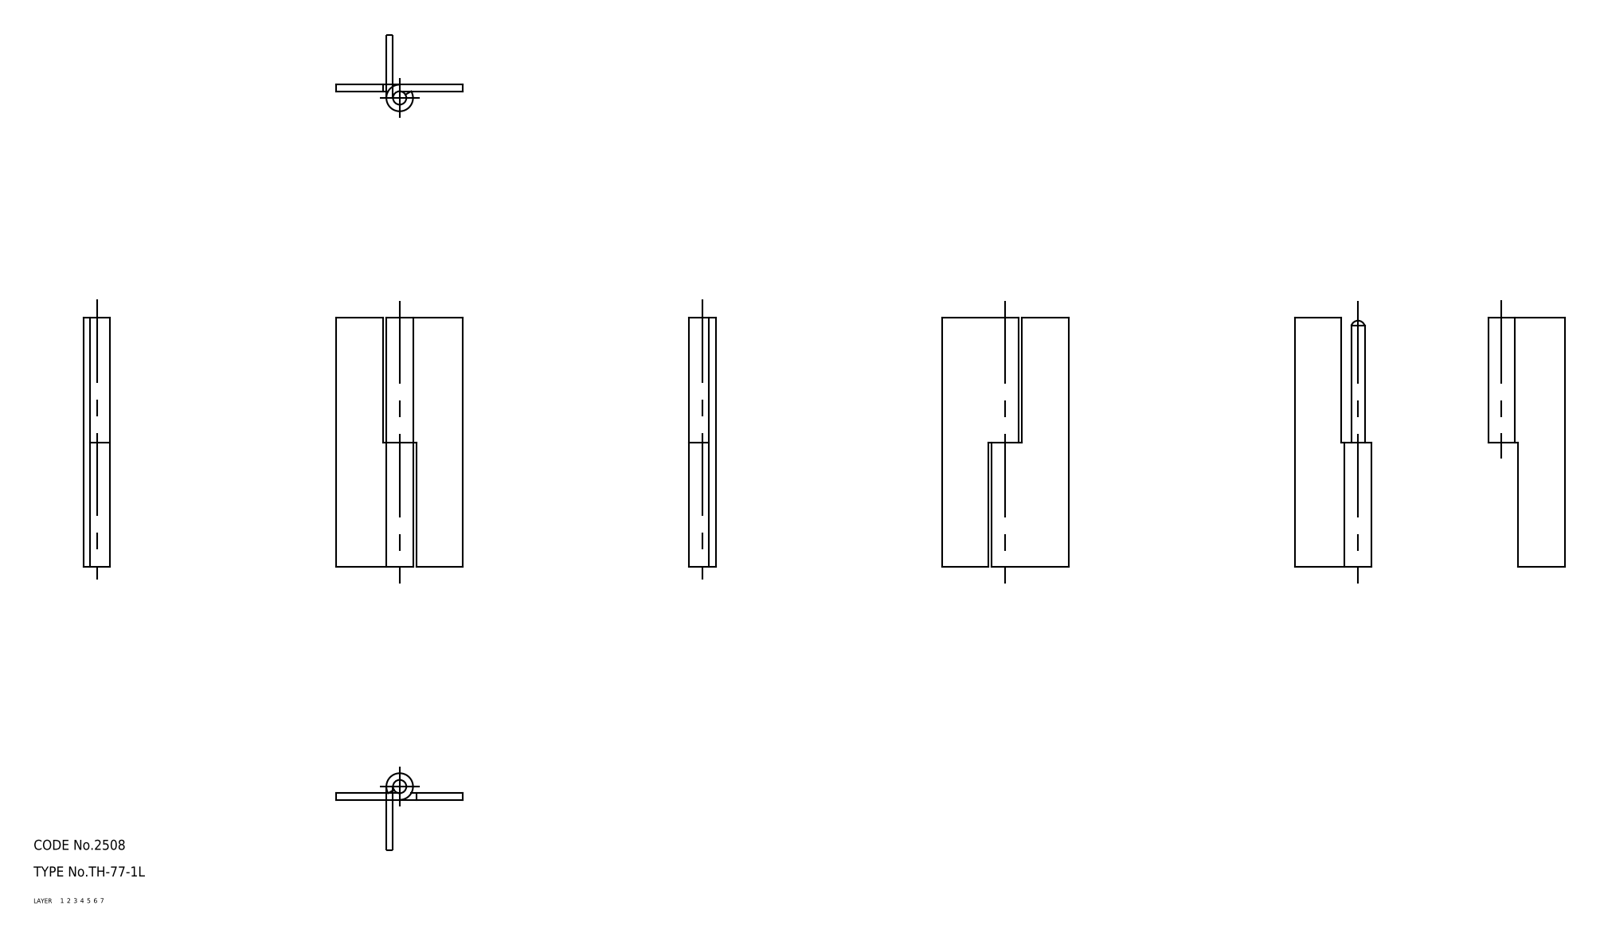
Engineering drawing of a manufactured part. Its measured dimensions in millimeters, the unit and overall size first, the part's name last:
Units: millimetres
Overall size (bounding box): 75 × 38 × 8
Volume: 8 224 mm³ · Surface area: 9 121 mm²
Bodies: 3 solids, 24 faces (0 planar, 0 cylindrical, 24 other)
Part name (STEP PRODUCT): shaft; hinge piece_B; hinge piece_A; TH_77_1L_15897_36
STEP written by: CADfix (AUTOMOTIVE_DESIGN)
